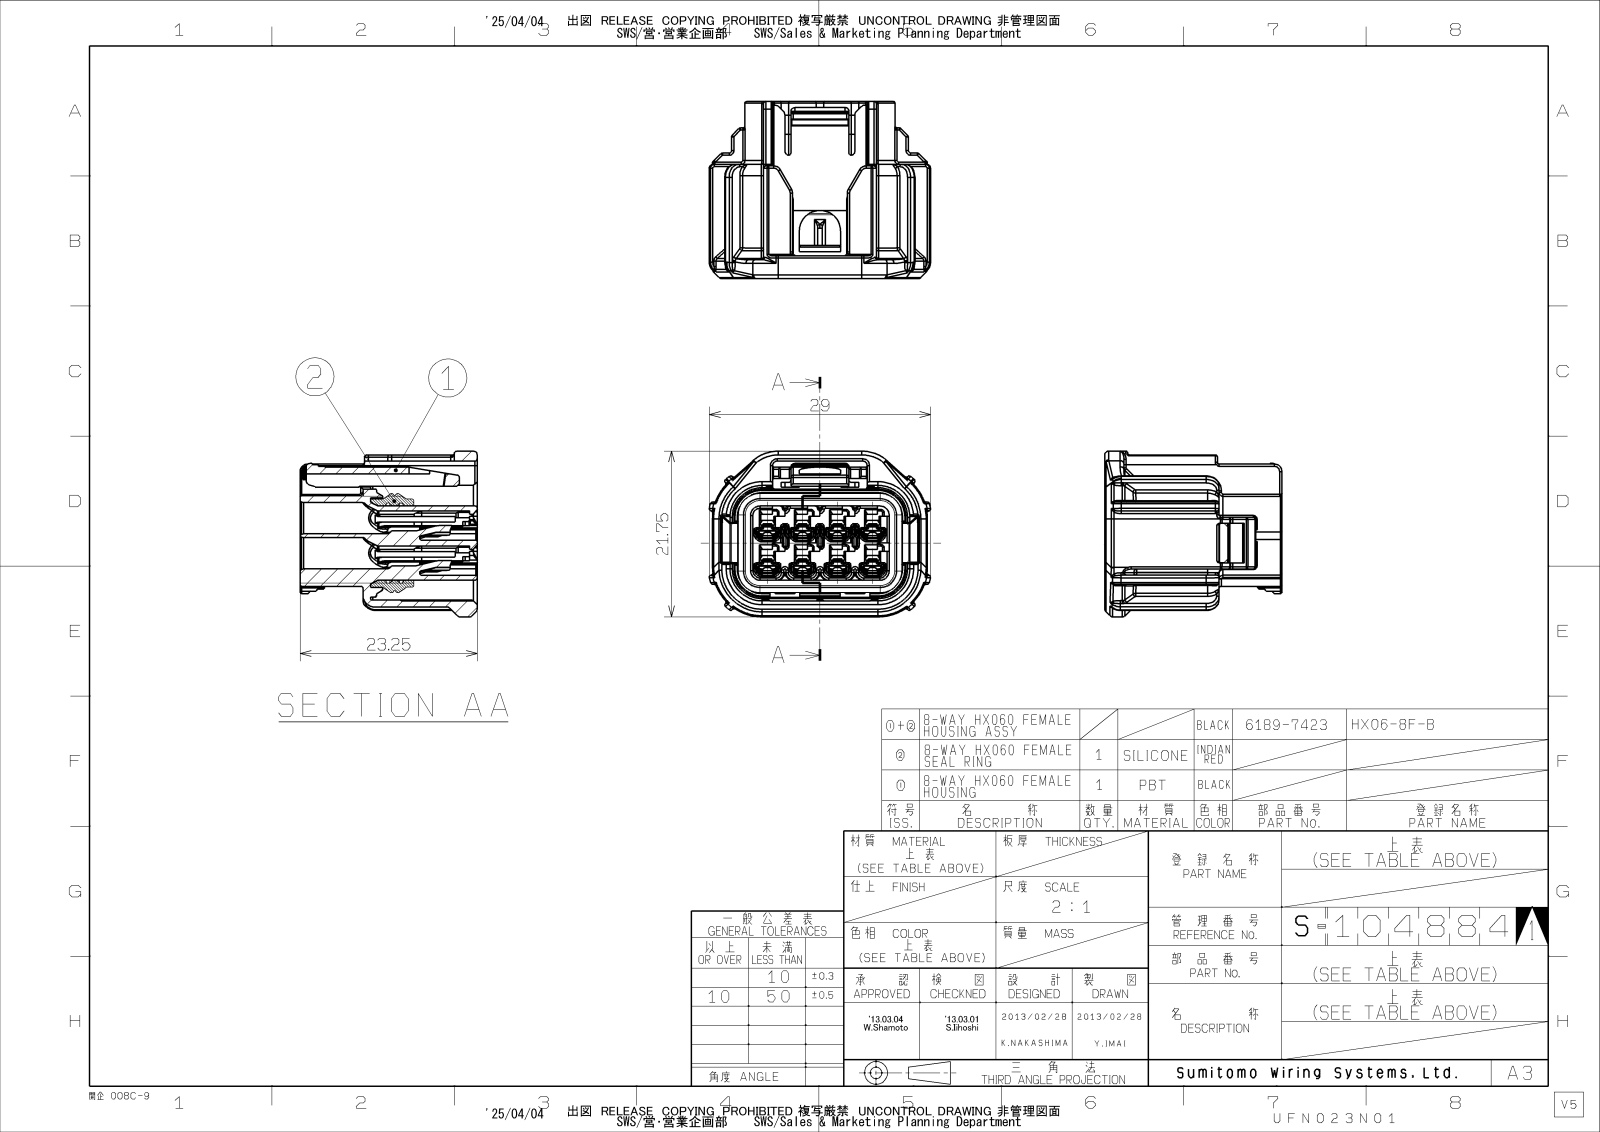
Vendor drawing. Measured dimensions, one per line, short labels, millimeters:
name: 6189-7423
written by: CATIA V5 STEP AP214 v2 (AUTOMOTIVE_DESIGN)
unit: mm
bodies: 1 solid, 373 faces (247 planar, 90 cylindrical, 36 other)
size: 29.15 × 23.25 × 21.75
volume: 6 478 mm³; area: 5 761 mm²
holes: 8× ⌀4.1
rounds: 10× R1.5, 9× R1, 6× R2.95, 6× R5, 4× R4.2, 4× R6.5, 4× R7.05, 2× R1.8
face distances: 1.2, 2.7, 0.8, 20.3, 6.7, 12.45, 3.5, 9.75, 1, 15
hole spacings: 4.6, 6.51, 9.2, 10.29, 13.8, 14.55
